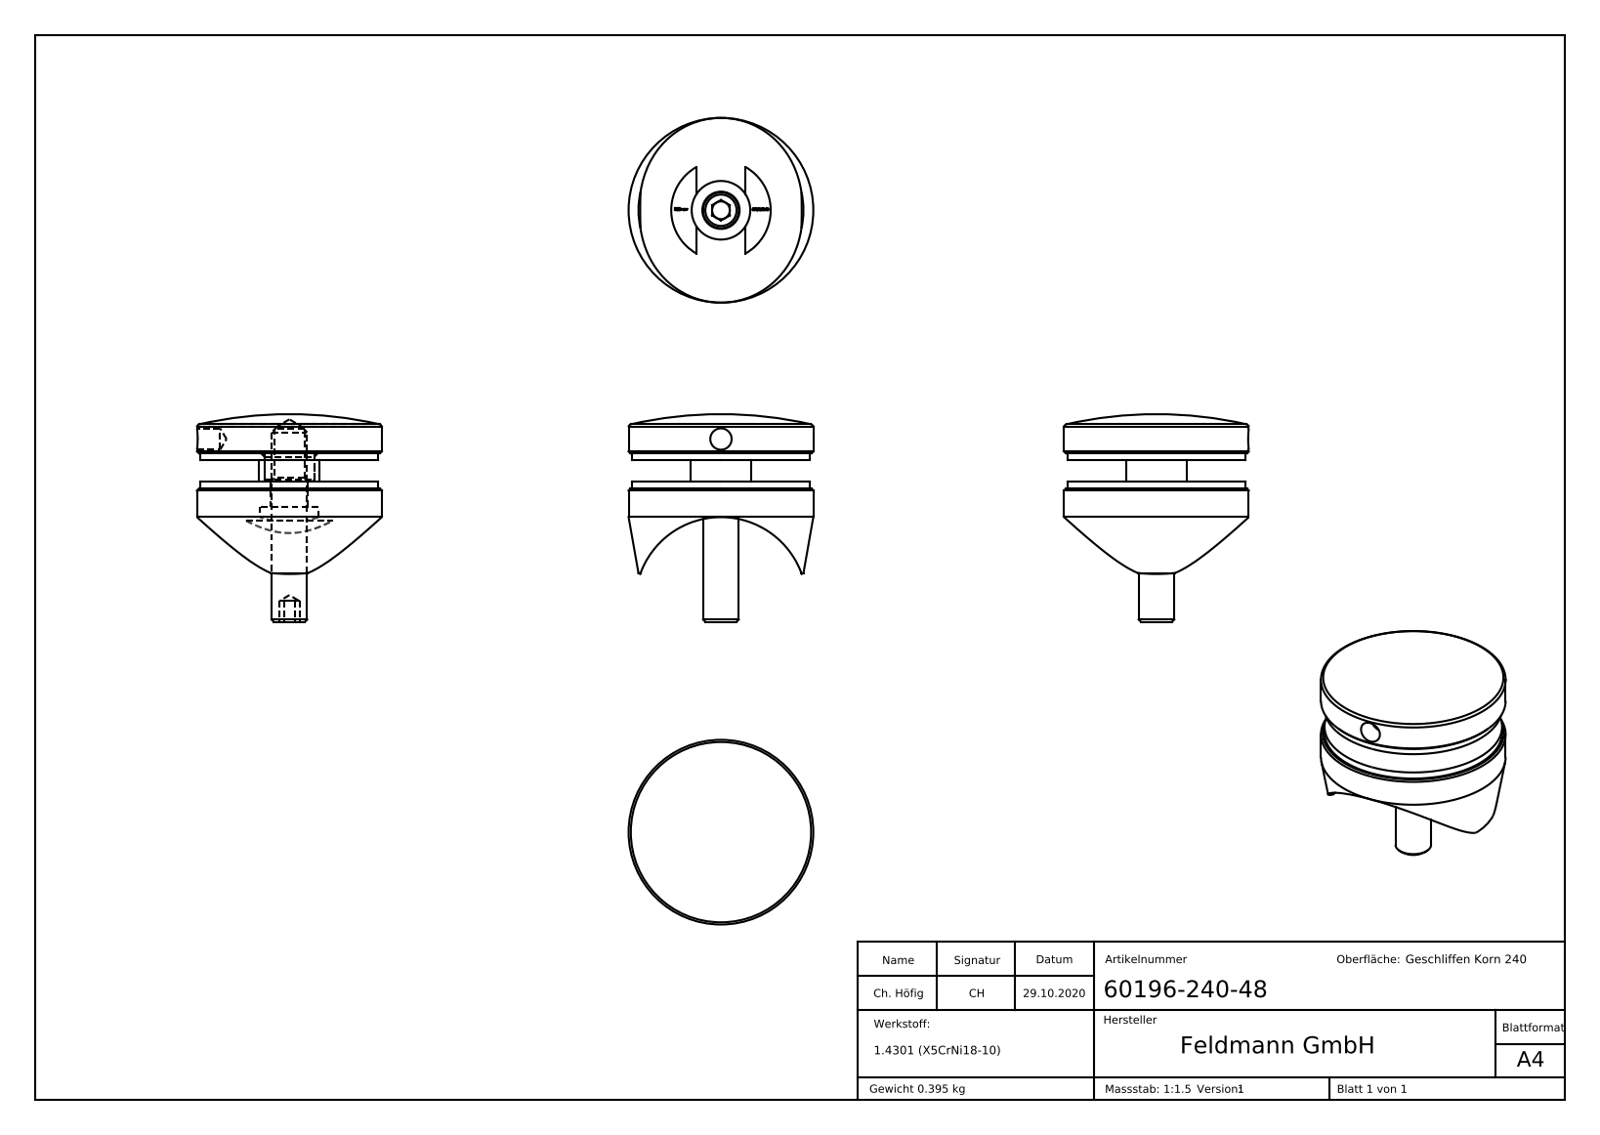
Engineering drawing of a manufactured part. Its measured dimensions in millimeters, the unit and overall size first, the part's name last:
Units: millimetres
Overall size (bounding box): 110 × 52 × 52
Round holes (diameter × count): ⌀6 ×1, ⌀8.5 ×1, ⌀10.5 ×1, ⌀14 ×1, ⌀16.5 ×1
Round bosses / shafts (diameter × count): ⌀52 ×1, ⌀50 ×1, ⌀17 ×1, ⌀10 ×1
Partial cylindrical surfaces — rounded edges, fillets, slot ends (radius × count): R14 ×1, R24.15 ×1
Main face-to-face distances: 2, 8, 10, 6, 9, 11, 17, 19, 5, 4
Volume: 55 283 mm³ · Surface area: 24 214 mm²
Bodies: 5 solids, 342 faces (166 planar, 29 cylindrical, 147 other)
Part name (STEP PRODUCT): 60196-240-48; 6019X-240 Konfig Teil2_60196-240-48 Teil2; DIN913; 6019X-240 Konfig Teil3 (+7 more)
STEP written by: SolidWorks 2018 (CONFIG_CONTROL_DESIGN)
